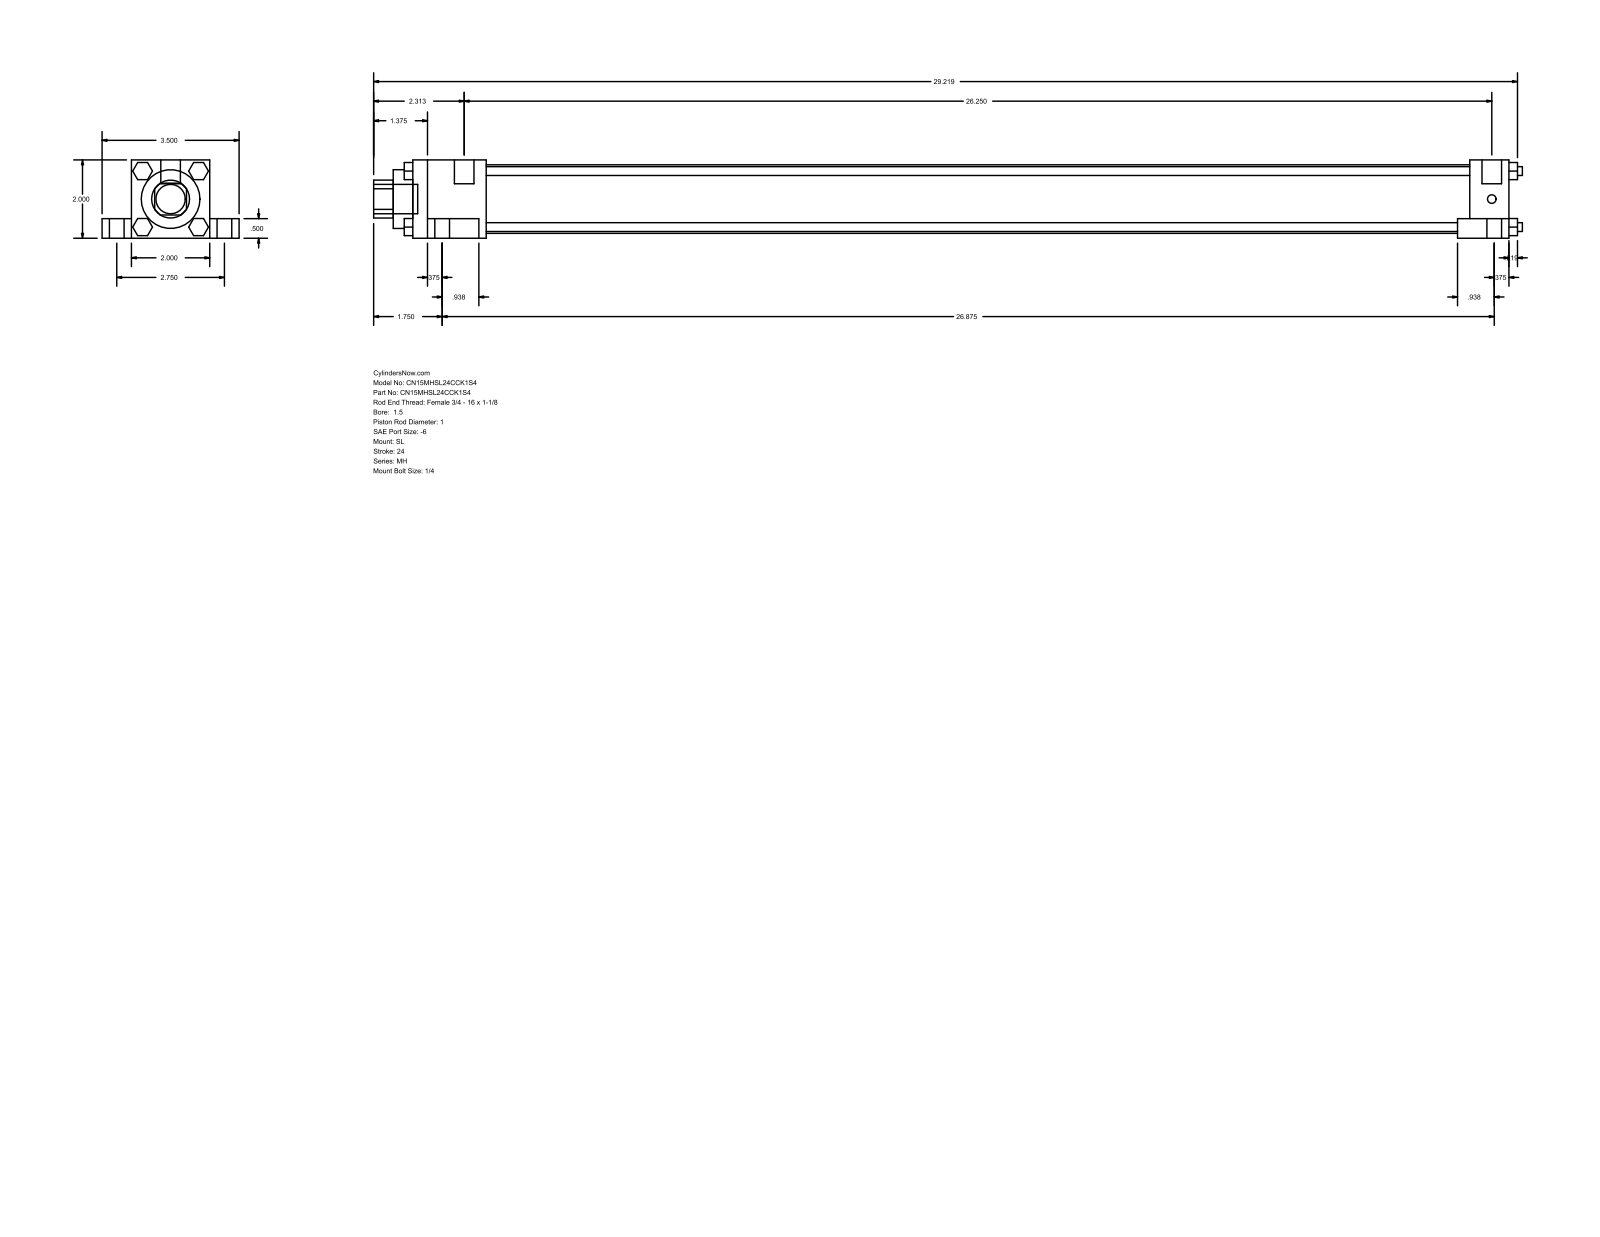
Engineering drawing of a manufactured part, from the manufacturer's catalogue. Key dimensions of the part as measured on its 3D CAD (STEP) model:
Part name (STEP PRODUCT): MH_SL__0150_1
STEP written by: GSSL Pune (CONFIG_CONTROL_DESIGN)
Units: millimetres
Bodies: 0 solids, 148 faces (112 planar, 36 cylindrical, 0 other)
Overall size (bounding box): 745.33 × 88.9 × 50.8
Round holes (diameter × count): ⌀25.4 ×1, ⌀38.1 ×1, ⌀44.45 ×1
Round bosses / shafts (diameter × count): ⌀15.88 ×4, ⌀9.53 ×4, ⌀5.71 ×4, ⌀5.56 ×4, ⌀12.7 ×2, ⌀19.05 ×1
Partial cylindrical surfaces — rounded edges, fillets, slot ends (radius × count): R12.29 ×1
Main face-to-face distances: 50.8, 12.7, 38.1, 19.05, 69.85, 711.2, 25.4, 9.52, 33.34, 668.34
